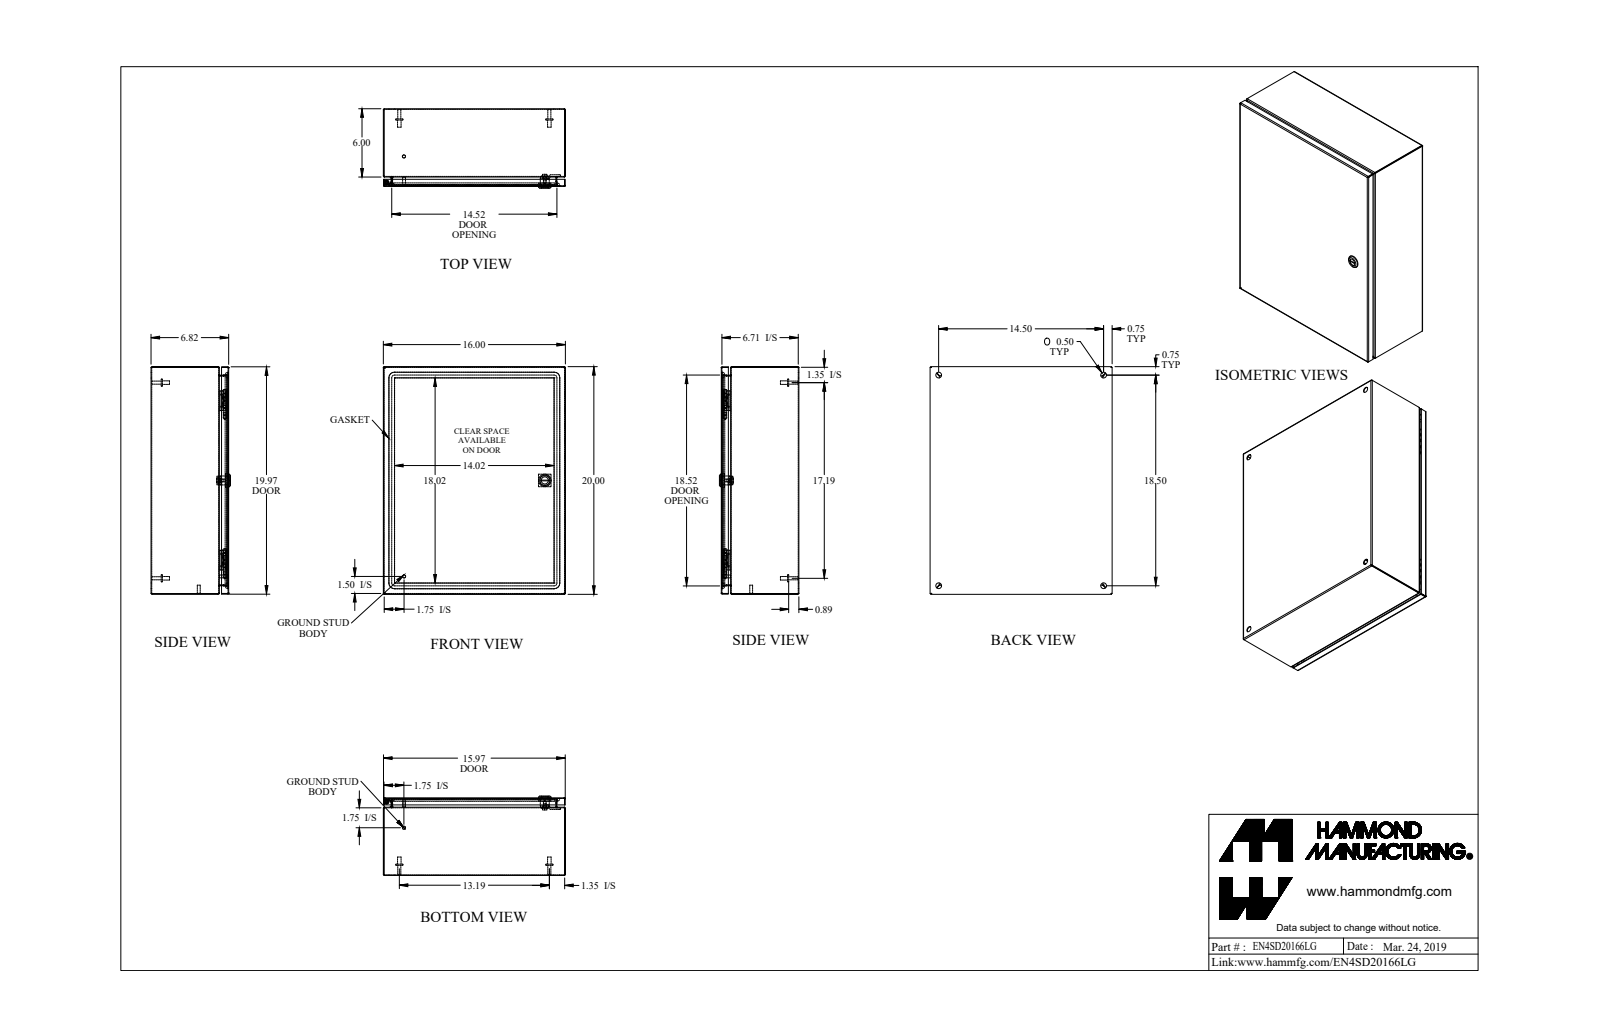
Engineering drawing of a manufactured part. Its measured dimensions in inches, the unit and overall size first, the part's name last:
Units: inches
Overall size (bounding box): 20 × 16 × 6.982
Round holes (diameter × count): ⌀0.5 ×4, ⌀0.172 ×1, ⌀0.232 ×1, ⌀0.24 ×1, ⌀0.242 ×1, ⌀0.625 ×1, ⌀0.785 ×1
Round bosses / shafts (diameter × count): ⌀0.625 ×4, ⌀0.313 ×4, ⌀0.27 ×4, ⌀0.281 ×2, ⌀0.25 ×2, ⌀1.1 ×1, ⌀0.525 ×1, ⌀0.455 ×1
Partial cylindrical surfaces — rounded edges, fillets, slot ends (radius × count): R0.029 ×21, R0.086 ×21, R0.25 ×16, R19 ×8, R0.006 ×4, R0.062 ×4, R0.499 ×4, R0.125 ×2
Main face-to-face distances: 0.057, 6.765, 6.708, 6.822, 15.943, 19.943, 15.886, 16, 19.886, 20
Hole centre spacings: 14.5, 18.5, 23.506, 9.31, 9.311, 16.316, 16.317
Volume: 76.29 in³ · Surface area: 2 585 in²
Bodies: 21 solids, 634 faces (285 planar, 213 cylindrical, 136 other)
Part name (STEP PRODUCT): EN4SD20166LG_Default
STEP written by: SolidWorks 2019 (CONFIG_CONTROL_DESIGN)
